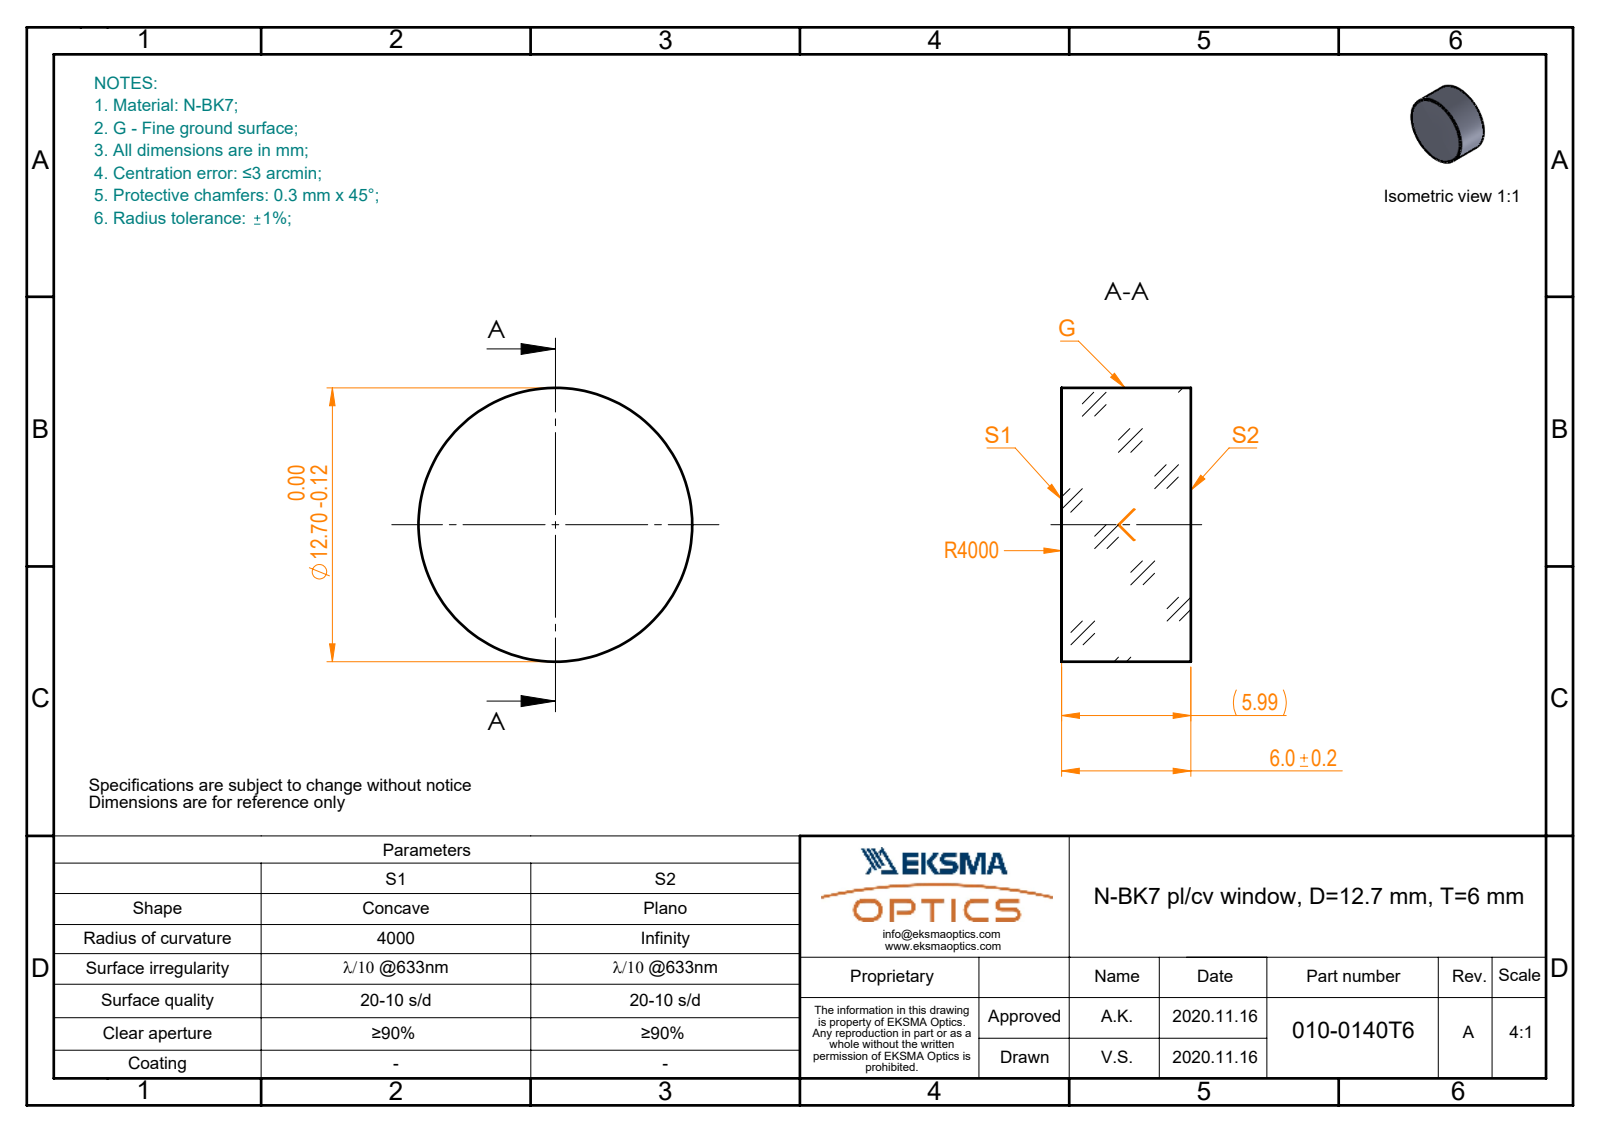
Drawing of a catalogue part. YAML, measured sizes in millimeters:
part_name: "010-0140T6_N-BK7_PCV_window"
step_written_by: "SolidWorks 2019 (CONFIG_CONTROL_DESIGN)"
units: millimeters
bodies: {solids: 1, faces: 5, planar: 1, cylindrical: 2, other: 2}
overall_size: [12.7, 12.7, 6]
volume: 760
surface_area: 493
round_bosses_or_shafts:
  - {diameter: 12.7, count: 1}
